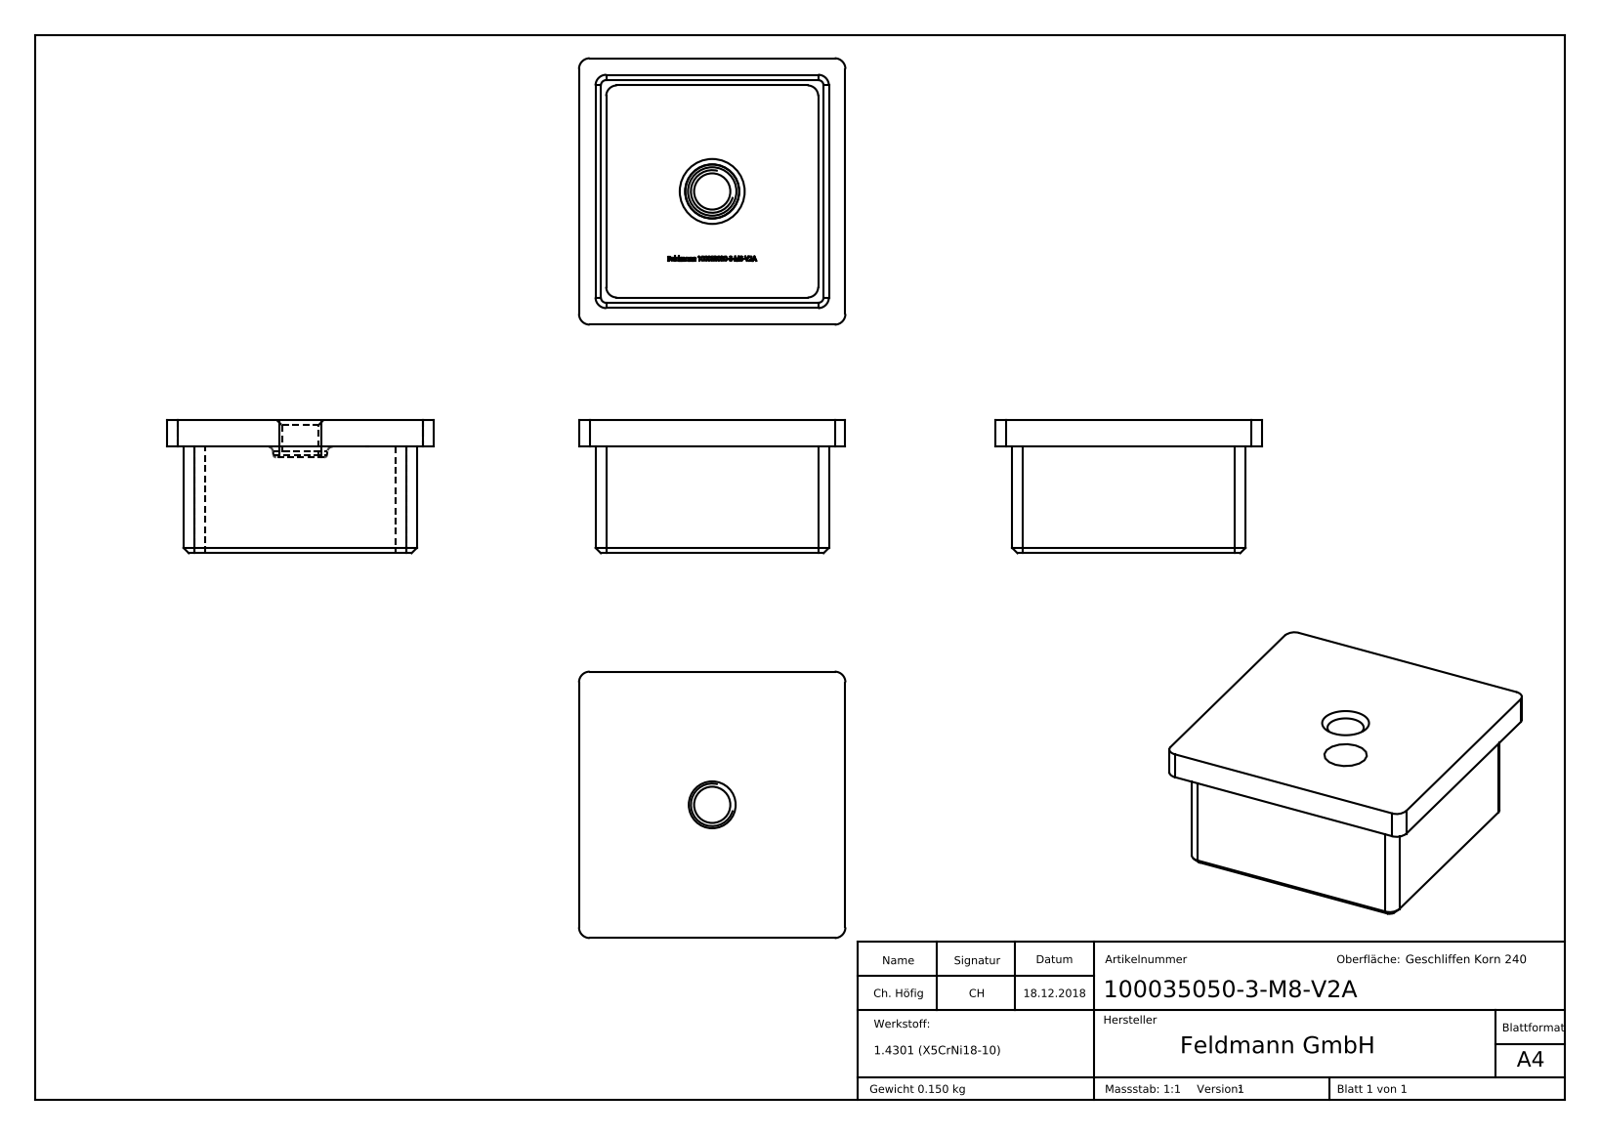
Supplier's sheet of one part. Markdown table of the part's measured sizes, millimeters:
| quantity | value |
| --- | --- |
| part name | 100035050-3-M8-V2A |
| STEP written by | SolidWorks 2015 (CONFIG_CONTROL_DESIGN) |
| units | millimeters |
| bodies | 1 solid, 371 faces (185 planar, 14 cylindrical, 172 other) |
| overall size | 50 × 50 × 25 |
| volume | 18 987 mm³ |
| surface area | 12 541 mm² |
| round holes (diameter × count) | 6.8 × 1 |
| partial cylindrical surfaces (radius × count) | 2 × 12 |
| main face-to-face distances | 2, 41.8, 5, 43.8, 39.8, 3.1, 5.1, 44.9, 46.9, 50 |
